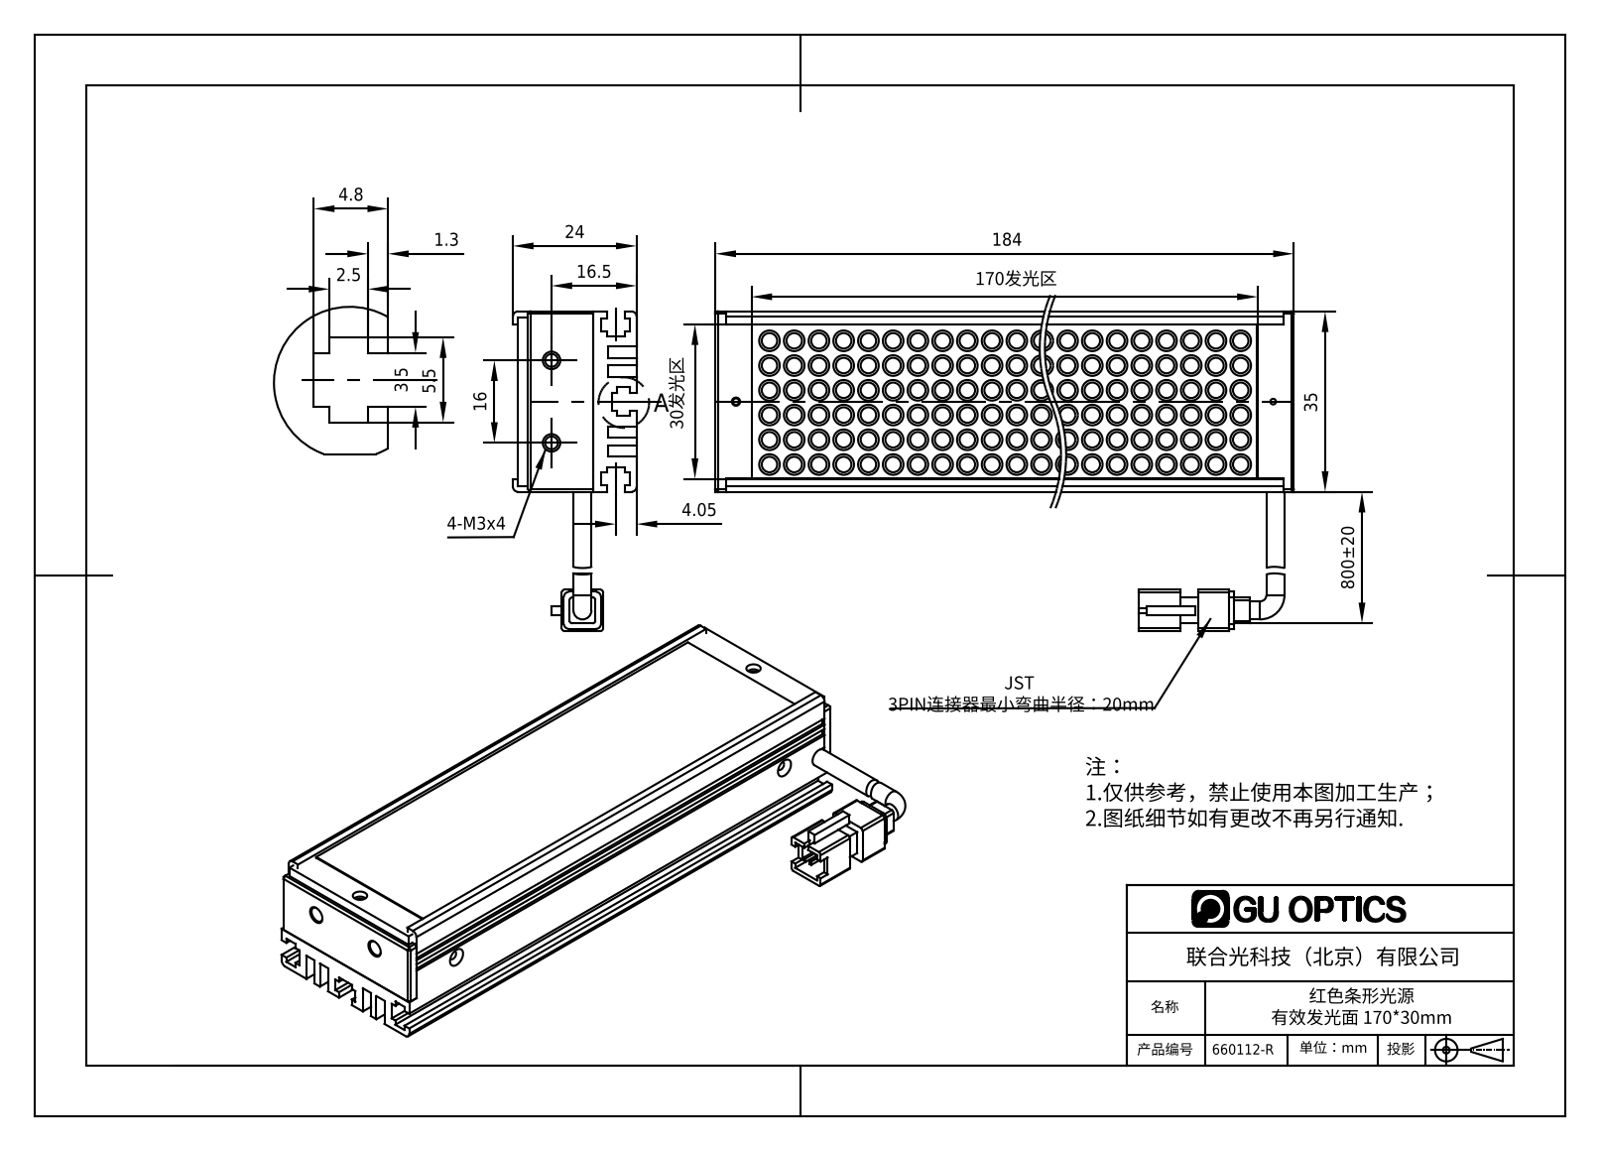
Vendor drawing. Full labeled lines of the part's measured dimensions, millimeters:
Part name (STEP PRODUCT): 660112-R
STEP written by: SolidWorks 2016 (AUTOMOTIVE_DESIGN)
Units: millimetres
Bodies: 8 solids, 1721 faces (477 planar, 927 cylindrical, 317 other)
Overall size (bounding box): 184 × 62 × 24
Volume: 82 743 mm³ · Surface area: 93 944 mm²
Round holes (diameter × count): ⌀1.6 ×5, ⌀1.7 ×3, ⌀1.5 ×2, ⌀2.5 ×2, ⌀2.8 ×2, ⌀3 ×2, ⌀1.1 ×1, ⌀1.25 ×1, ⌀2 ×1
Round bosses / shafts (diameter × count): ⌀4 ×210, ⌀3 ×210, ⌀3.5 ×2
Partial cylindrical surfaces — rounded edges, fillets, slot ends (radius × count): R1 ×12, R0.5 ×8, R1.65 ×1
Main face-to-face distances: 2, 2.2, 8.6, 1, 2.5, 12.6, 14.6, 9, 4, 10.6
Hole centre spacings: 176, 7, 28.05, 28.52, 60, 88.01, 88.17, 148.01
